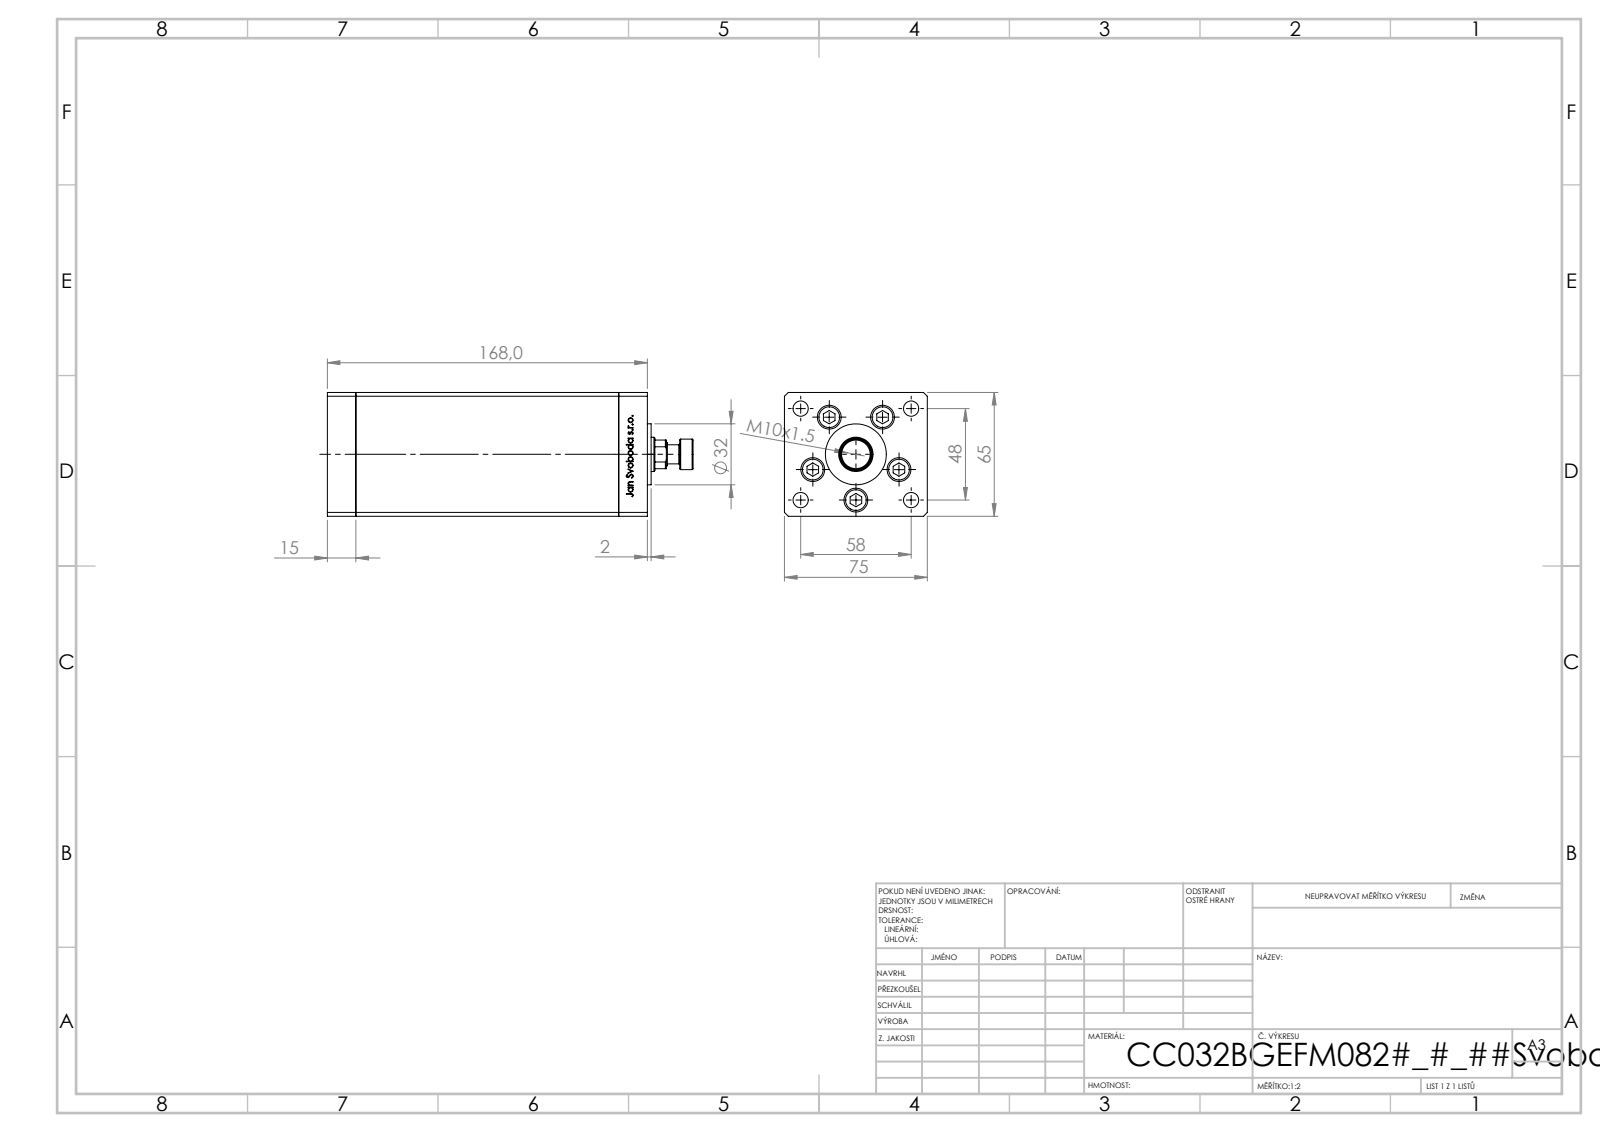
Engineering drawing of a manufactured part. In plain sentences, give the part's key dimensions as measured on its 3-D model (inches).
The part is named "ALLEN BOLT; V220C_B MIDDLE; V220C_VC_B; V220C BACK_B (+2 more)". Its 3-D file was written by "SolidWorks 2019 (CONFIG_CONTROL_DESIGN)". It is 15 solids with 1199 faces: 466 planar, 151 cylindrical and 582 other. Overall it measures 7.559 by 2.953 by 2.559 inches. Its volume is 44.71 cubic inches and its surface area 200.4 square inches. Round holes: 5 of diameter 0.354, 5 of diameter 0.492, 4 of diameter 0.315, 2 of diameter 0.079, 2 of diameter 0.518, 1 of diameter 0.335, 1 of diameter 0.709. Round bosses or shafts: 5 of diameter 0.315, 1 of diameter 1.26, 1 of diameter 0.63, 1 of diameter 0.394. Partial cylindrical surfaces (rounded edges, fillets, slot ends): 2 of radius 0.037, 1 of radius 0.335. The main face-to-face distances are 2.953, 2.559, 0.591, 5.433, 6.024, 6.614, 1.102, 2.146, 0.413, 0.512. The hole center spacings are 0.945, 1.482, 0.617, 0.678, 1.091, 1.135, 1.142, 1.285.
